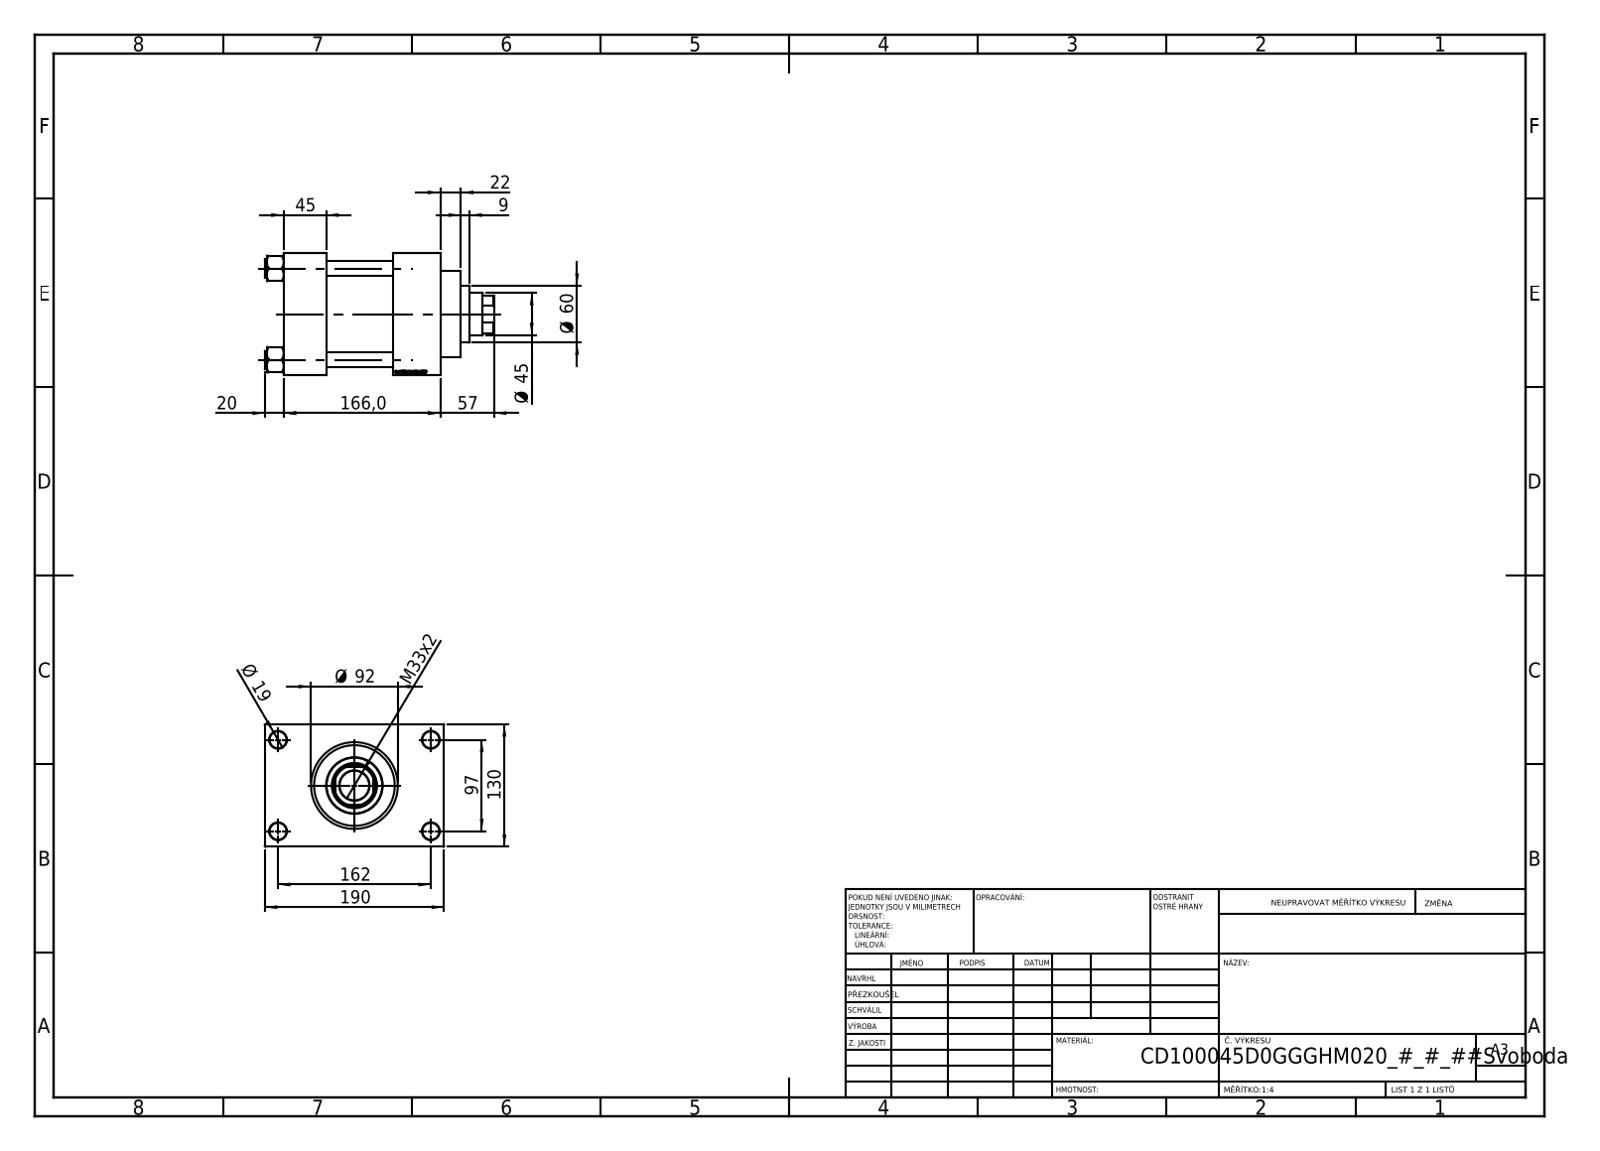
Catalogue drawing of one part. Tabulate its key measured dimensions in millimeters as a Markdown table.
| quantity | value |
| --- | --- |
| part name | V215CD_VCP_D; V215CD_VC_A; V215CD_D_TYCINKA; V215CD_NUT_M5_D (+1 more) |
| STEP written by | SolidWorks 2019 (CONFIG_CONTROL_DESIGN) |
| units | millimeters |
| bodies | 11 solids, 1152 faces (545 planar, 89 cylindrical, 518 other) |
| overall size | 243 × 190 × 130 |
| volume | 2 607 000 mm³ |
| surface area | 352 394 mm² |
| round holes (diameter × count) | 16 × 4, 18 × 4, 7 × 2, 26.44 × 2, 35 × 2, 31.5 × 1, 45 × 1, 48 × 1, 76 × 1, 85.5 × 1, 100 × 1 |
| round bosses / shafts (diameter × count) | 19 × 4, 106 × 1, 92 × 1, 60 × 1 |
| partial cylindrical surfaces (radius × count) | 22 × 1 |
| main face-to-face distances | 130, 45, 116, 71, 166, 121, 50, 30, 160, 20 |
| hole center spacings | 32.55, 68.52, 94.41, 96.9, 102.27, 129.45, 161.73, 97 |
